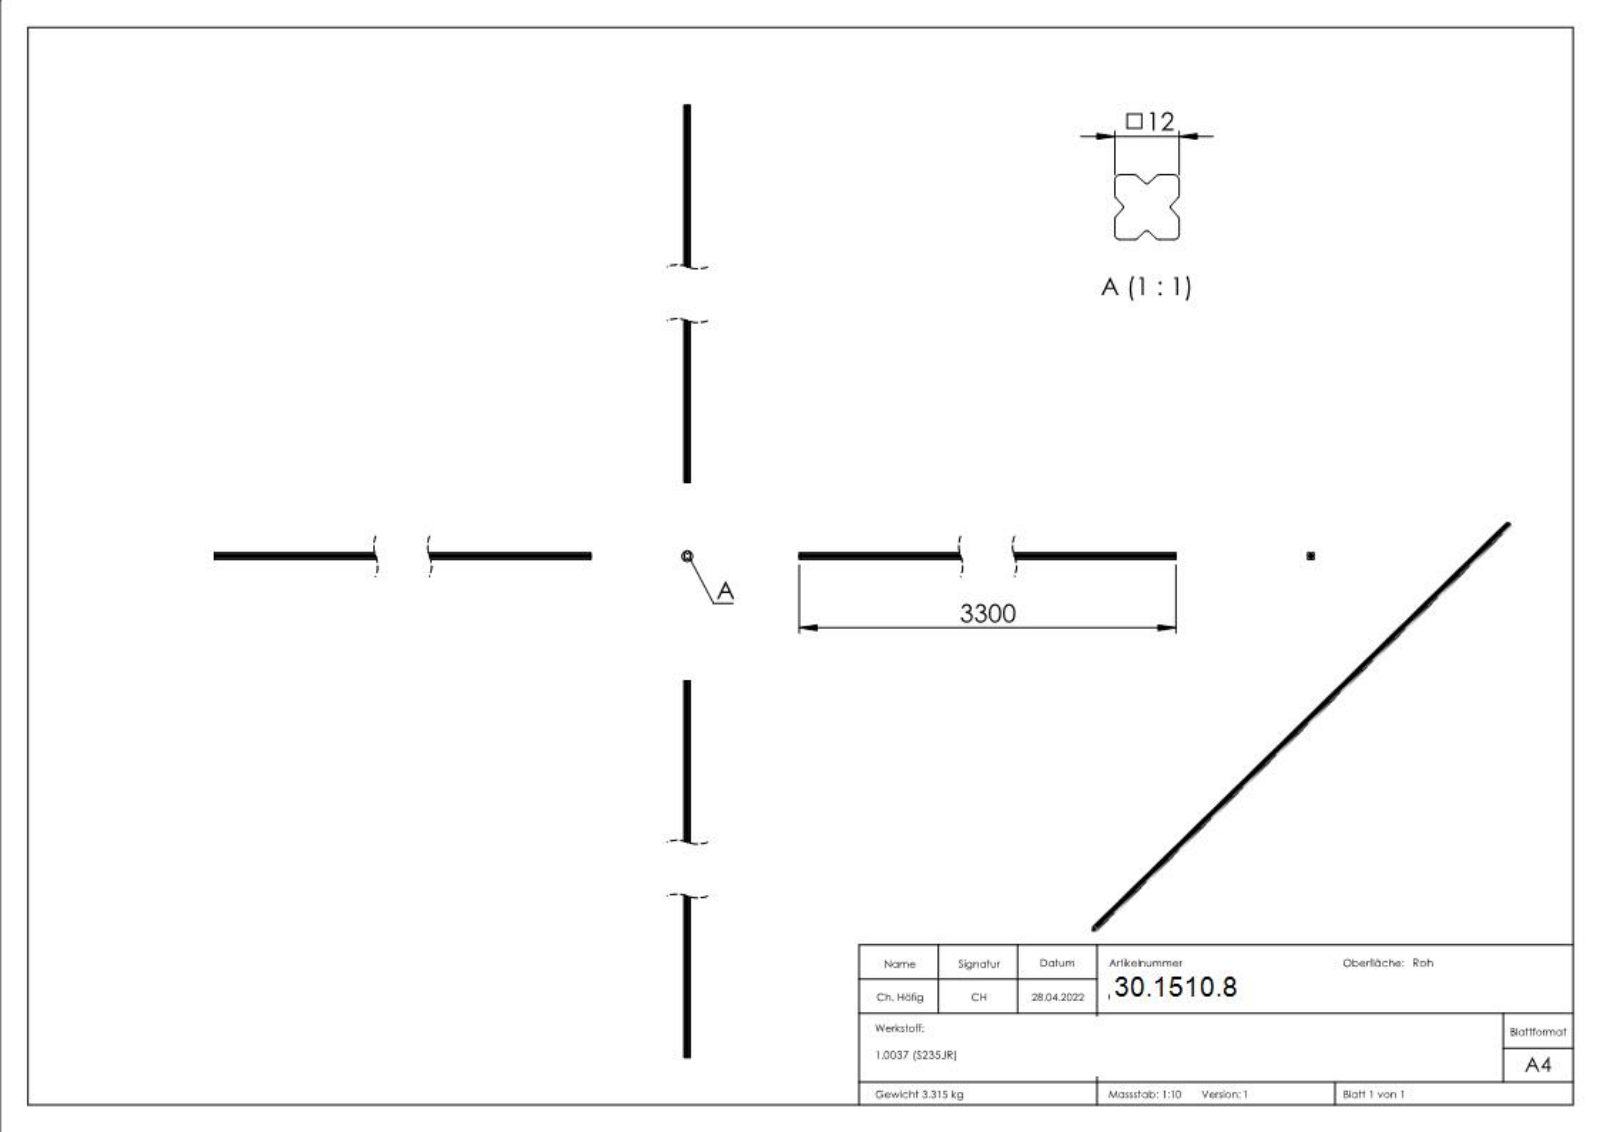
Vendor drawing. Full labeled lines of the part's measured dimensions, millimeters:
Part name (STEP PRODUCT): 6004
STEP written by: SolidWorks 2018 (CONFIG_CONTROL_DESIGN)
Units: millimetres
Bodies: 1 solid, 241 faces (130 planar, 16 cylindrical, 95 other)
Overall size (bounding box): 3300 × 12 × 12
Volume: 424 979 mm³ · Surface area: 168 327 mm²
Partial cylindrical surfaces — rounded edges, fillets, slot ends (radius × count): R0.8 ×8, R0.5 ×4, R1 ×4
Main face-to-face distances: 12, 6.24, 3300, 3299.9, 2.45, 4.75, 7.25, 0.32, 1.62, 0.34
